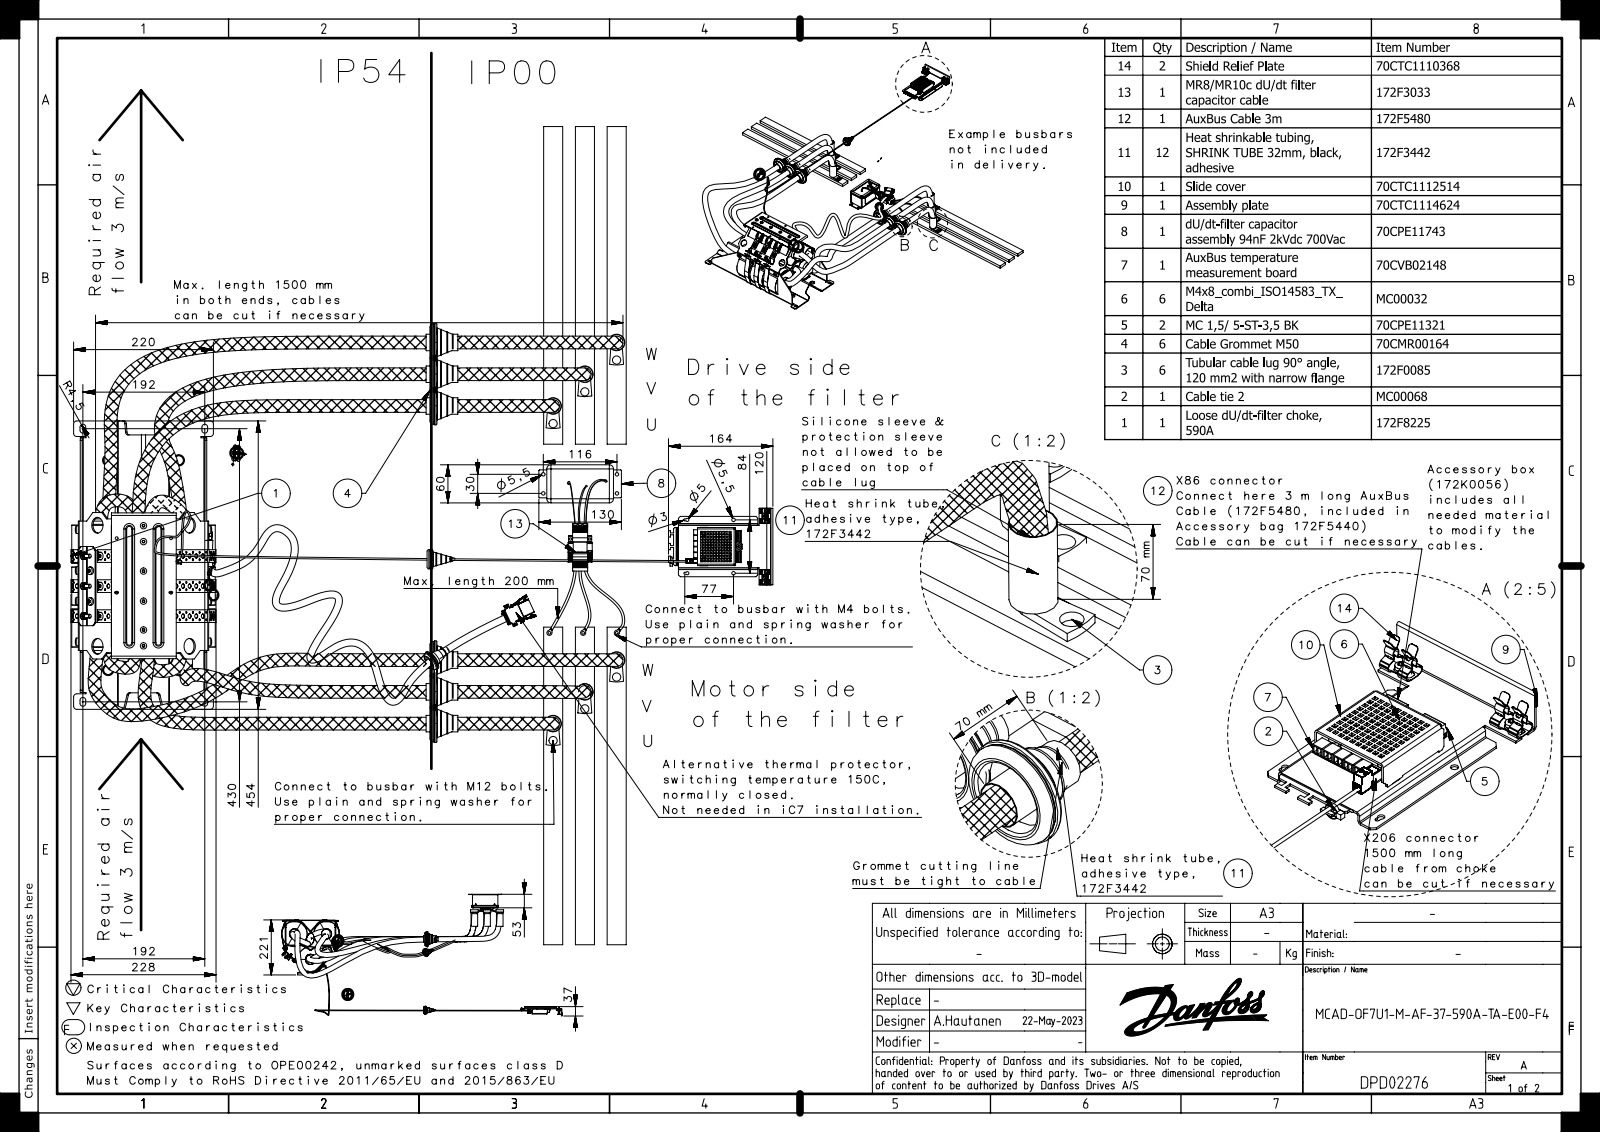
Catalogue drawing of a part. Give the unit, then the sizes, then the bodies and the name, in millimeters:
Units: millimetres
Overall size (bounding box): 1105.49 × 664.73 × 479.09
Round holes (diameter × count): ⌀2.9 ×12, ⌀1.6 ×8, ⌀4 ×8, ⌀5.5 ×6, ⌀13 ×6, ⌀15 ×6, ⌀42 ×6, ⌀3.3 ×5, ⌀4.5 ×4, ⌀25 ×4, ⌀40 ×4, ⌀1.8 ×3
Round bosses / shafts (diameter × count): ⌀1 ×15, ⌀26 ×12, ⌀2.8 ×10, ⌀60 ×6, ⌀58 ×6, ⌀50.2 ×6, ⌀17 ×6, ⌀10 ×6
Partial cylindrical surfaces — rounded edges, fillets, slot ends (radius × count): R0.1 ×92, R0.5 ×62, R0.25 ×59, R0.2 ×52, R1 ×43, R0.4 ×40, R2 ×38, R0.75 ×36
Main face-to-face distances: 3, 66, 60, 196.2, 6, 126, 132, 193.2, 2, 66.2
Hole centre spacings: 3.5, 7, 32.5, 29, 36, 5.08, 10.5, 25.5
Volume: 7 962 000 mm³ · Surface area: 2 246 000 mm²
Bodies: 155 solids, 6567 faces (4627 planar, 1327 cylindrical, 613 other)
Part name (STEP PRODUCT): 70CPE07576; 70CPE05327; 70CPE06034; PP20555 (+7 more)
STEP written by: SIEMENS PLM Software NX 1892 (AUTOMOTIVE_DESIGN)
